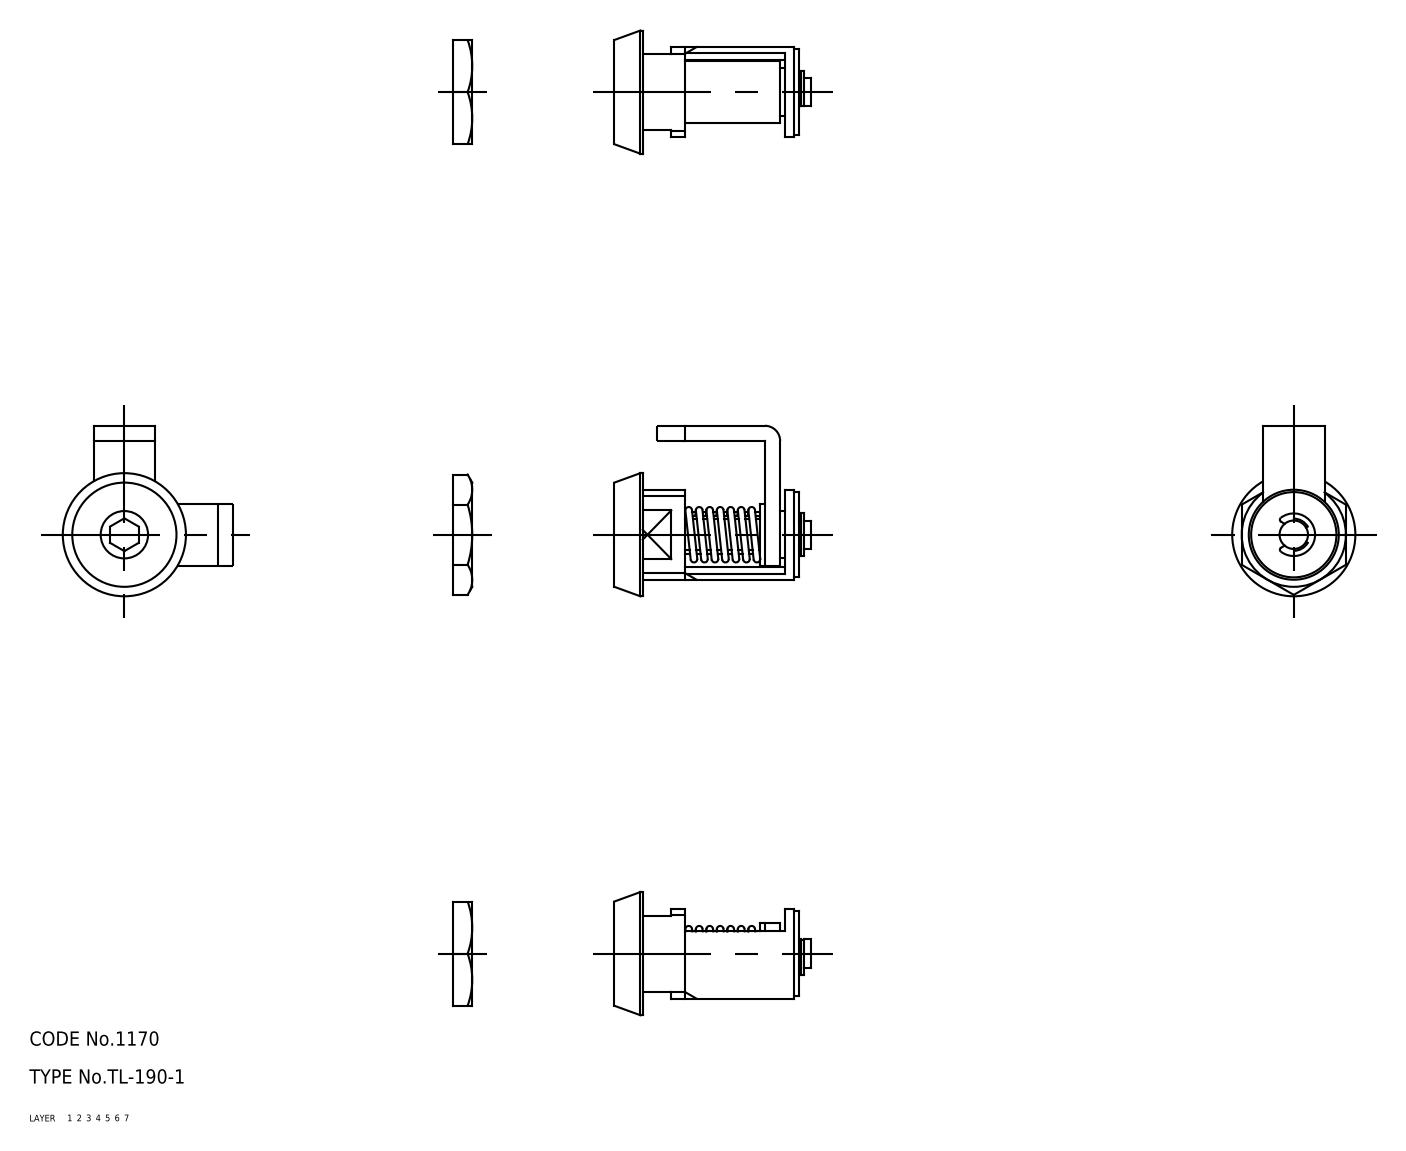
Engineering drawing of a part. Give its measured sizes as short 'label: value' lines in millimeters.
name: washer; spring; shaft; retainer (+5 more)
written by: CADfix (AUTOMOTIVE_DESIGN)
unit: mm
bodies: 9 solids, 138 faces (0 planar, 0 cylindrical, 138 other)
size: 41.5 × 36 × 26
volume: 9 557 mm³; area: 10 224 mm²
